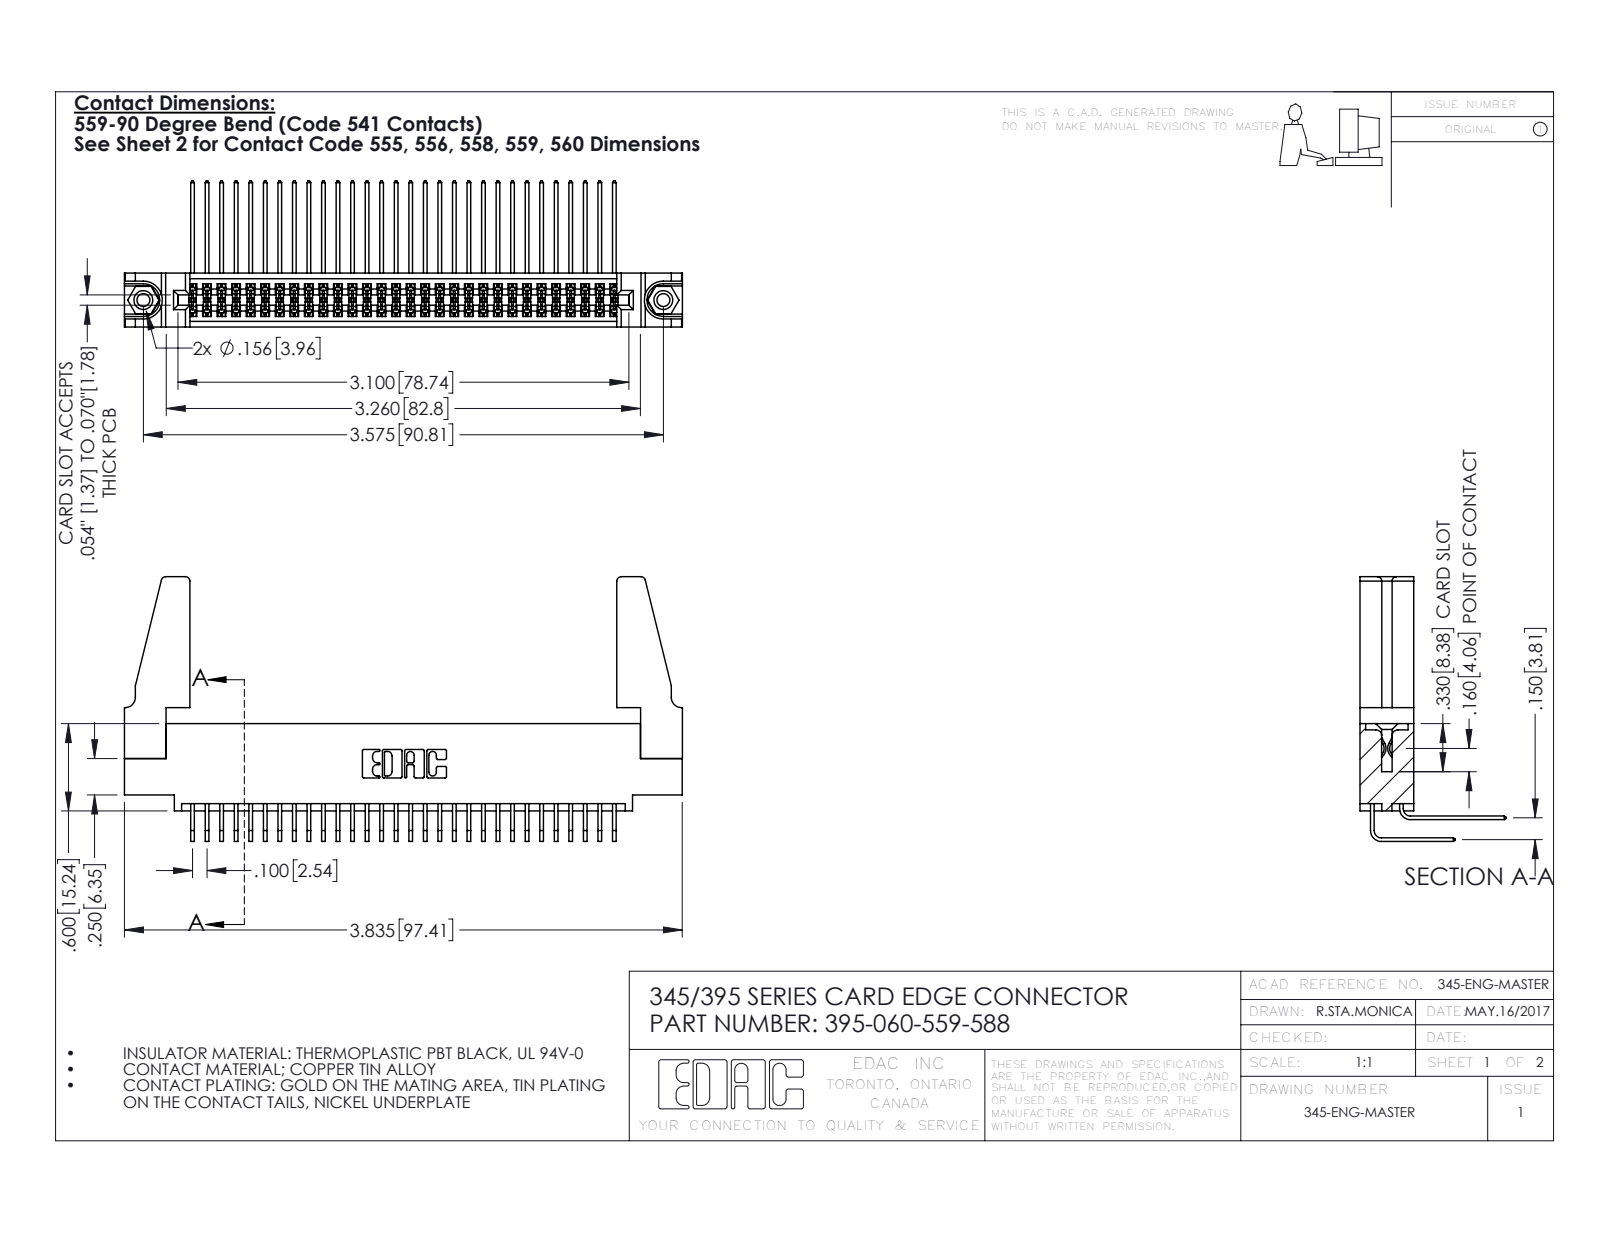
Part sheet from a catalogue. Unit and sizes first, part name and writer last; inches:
Units: inches
Overall size (bounding box): 3.836 × 1.819 × 1.005
Round holes (diameter × count): ⌀0.089 ×2, ⌀0.125 ×2, ⌀0.156 ×2, ⌀0.064 ×1
Round bosses / shafts (diameter × count): ⌀0.155 ×2
Partial cylindrical surfaces — rounded edges, fillets, slot ends (radius × count): R0.006 ×90, R0.01 ×22, R0.03 ×8, R0.007 ×6, R0.031 ×6, R0.026 ×3, R0.014 ×2, R0.019 ×2
Main face-to-face distances: 0.072, 0.298, 0.37, 0.2, 0.098, 0.272, 0.025, 0.225, 0.15, 0.175
Hole centre spacings: 0.27, 3.34, 3.575
Volume: 0.786 in³ · Surface area: 29.2 in²
Bodies: 65 solids, 3374 faces (2256 planar, 1102 cylindrical, 16 other)
Part name (STEP PRODUCT): 345-220-078_345-220-088; 345-292-001_558 559 Tail - 1; 345 Part_0.110 Offset - 0.156 Dia-TH; 345-292-001_559 Tail - 2 (+2 more)
STEP written by: SolidWorks 2016 (CONFIG_CONTROL_DESIGN)
